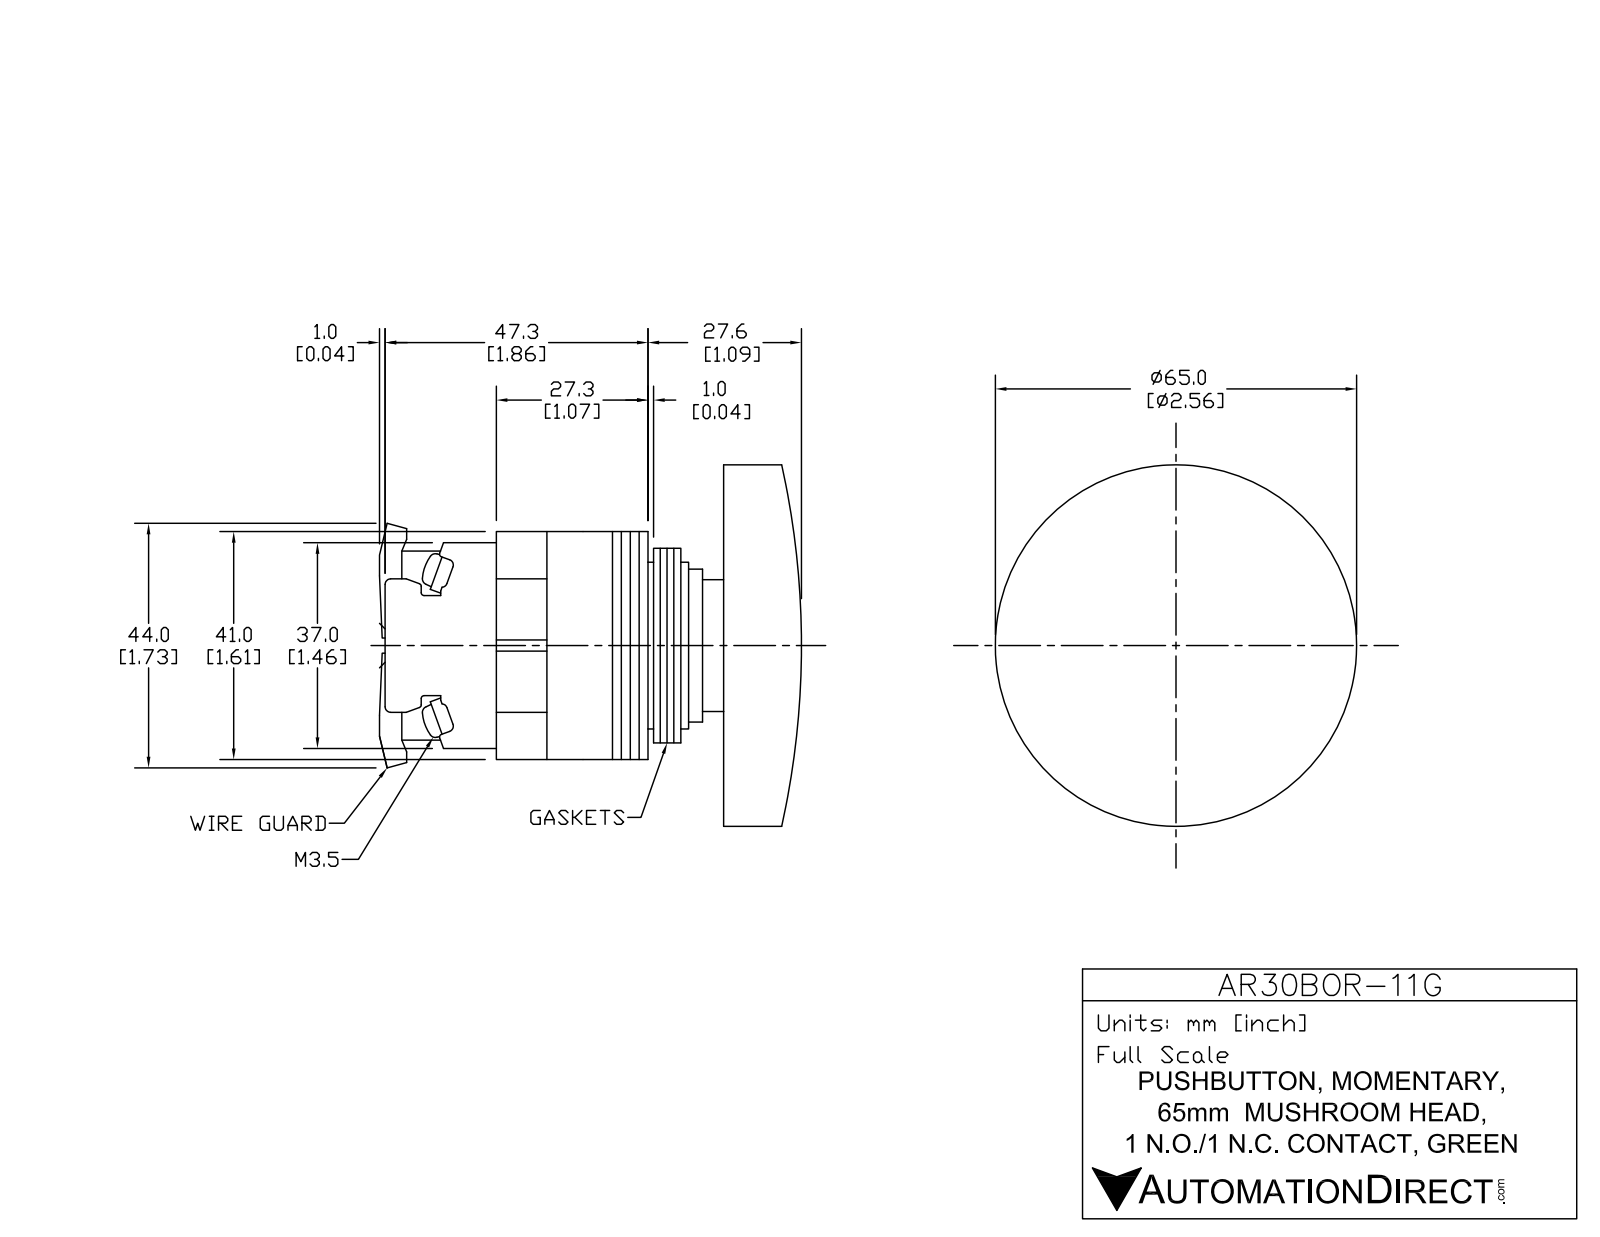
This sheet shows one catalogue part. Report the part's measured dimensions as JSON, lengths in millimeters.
{"part_name": "AR30B0R-11G", "step_written_by": "SolidWorks 2017 (AUTOMOTIVE_DESIGN)", "units": "millimeters", "bodies": {"solids": 20, "faces": 381, "planar": 236, "cylindrical": 127, "other": 18}, "overall_size": [76, 65, 65], "volume_mm3": 83080, "surface_area_mm2": 42286, "round_holes": [[3, 4], [24, 1], [30, 1], [60, 1]], "round_bosses_or_shafts": [[5, 4], [65, 1], [40, 1], [35, 1], [29.8, 1]], "partial_cylinders_radius": [[0.5, 16], [5, 10], [1.75, 8], [2, 4], [3, 4]], "face_to_face_distances": [1.6, 21, 16, 3.2, 41, 5, 1, 4.8, 36, 15.99], "hole_center_spacings": [21.92, 31, 43.84]}
